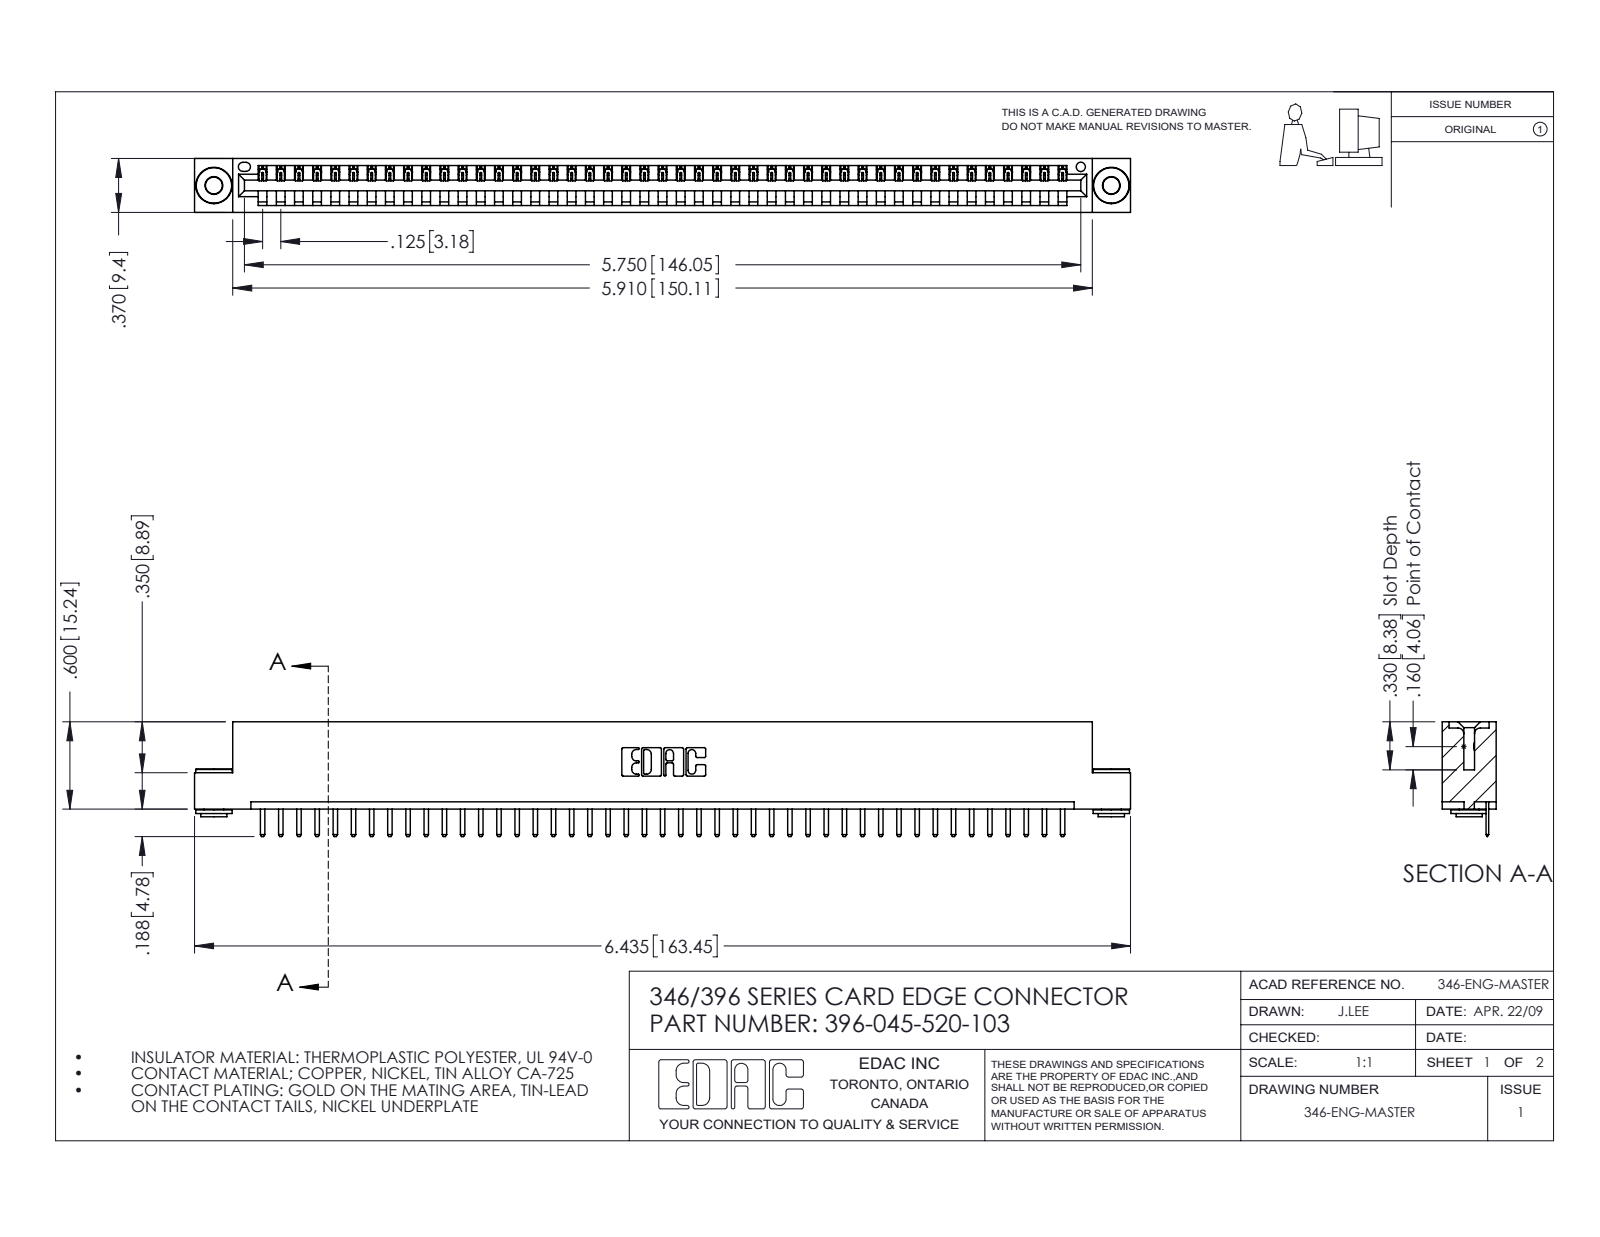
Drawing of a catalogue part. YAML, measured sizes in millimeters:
part_name: "346 Part_Flush Mounting Lugs - 0.156 Dia-TH; 345-250-002_345-250-002-102; 396-045-520-103; 345-292-001_345-293-120"
step_written_by: "SolidWorks 2016 (CONFIG_CONTROL_DESIGN)"
units: millimeters
bodies: {solids: 48, faces: 2950, planar: 1976, cylindrical: 966, other: 8}
overall_size: [163.4, 20, 9.4]
volume: 15600
surface_area: 19260
round_holes:
  - {diameter: 2.9, count: 2}
  - {diameter: 4, count: 2}
  - {diameter: 1.6, count: 1}
round_bosses_or_shafts:
  - {diameter: 6.4, count: 2}
  - {diameter: 4.6, count: 2}
  - {diameter: 3.5, count: 2}
partial_cylinders:
  - {radius: 0.3, count: 92}
  - {radius: 0.2, count: 90}
  - {radius: 0.3, count: 22}
  - {radius: 0.2, count: 6}
  - {radius: 0.8, count: 6}
  - {radius: 0.7, count: 3}
  - {radius: 0.8, count: 2}
  - {radius: 1, count: 2}
face_to_face_distances: [1.2, 8.2, 9.4, 6.4, 3.8, 5.6, 2.5, 4.4, 0.6, 1.8]
hole_center_spacings: [6.2, 151.4, 156.7]
